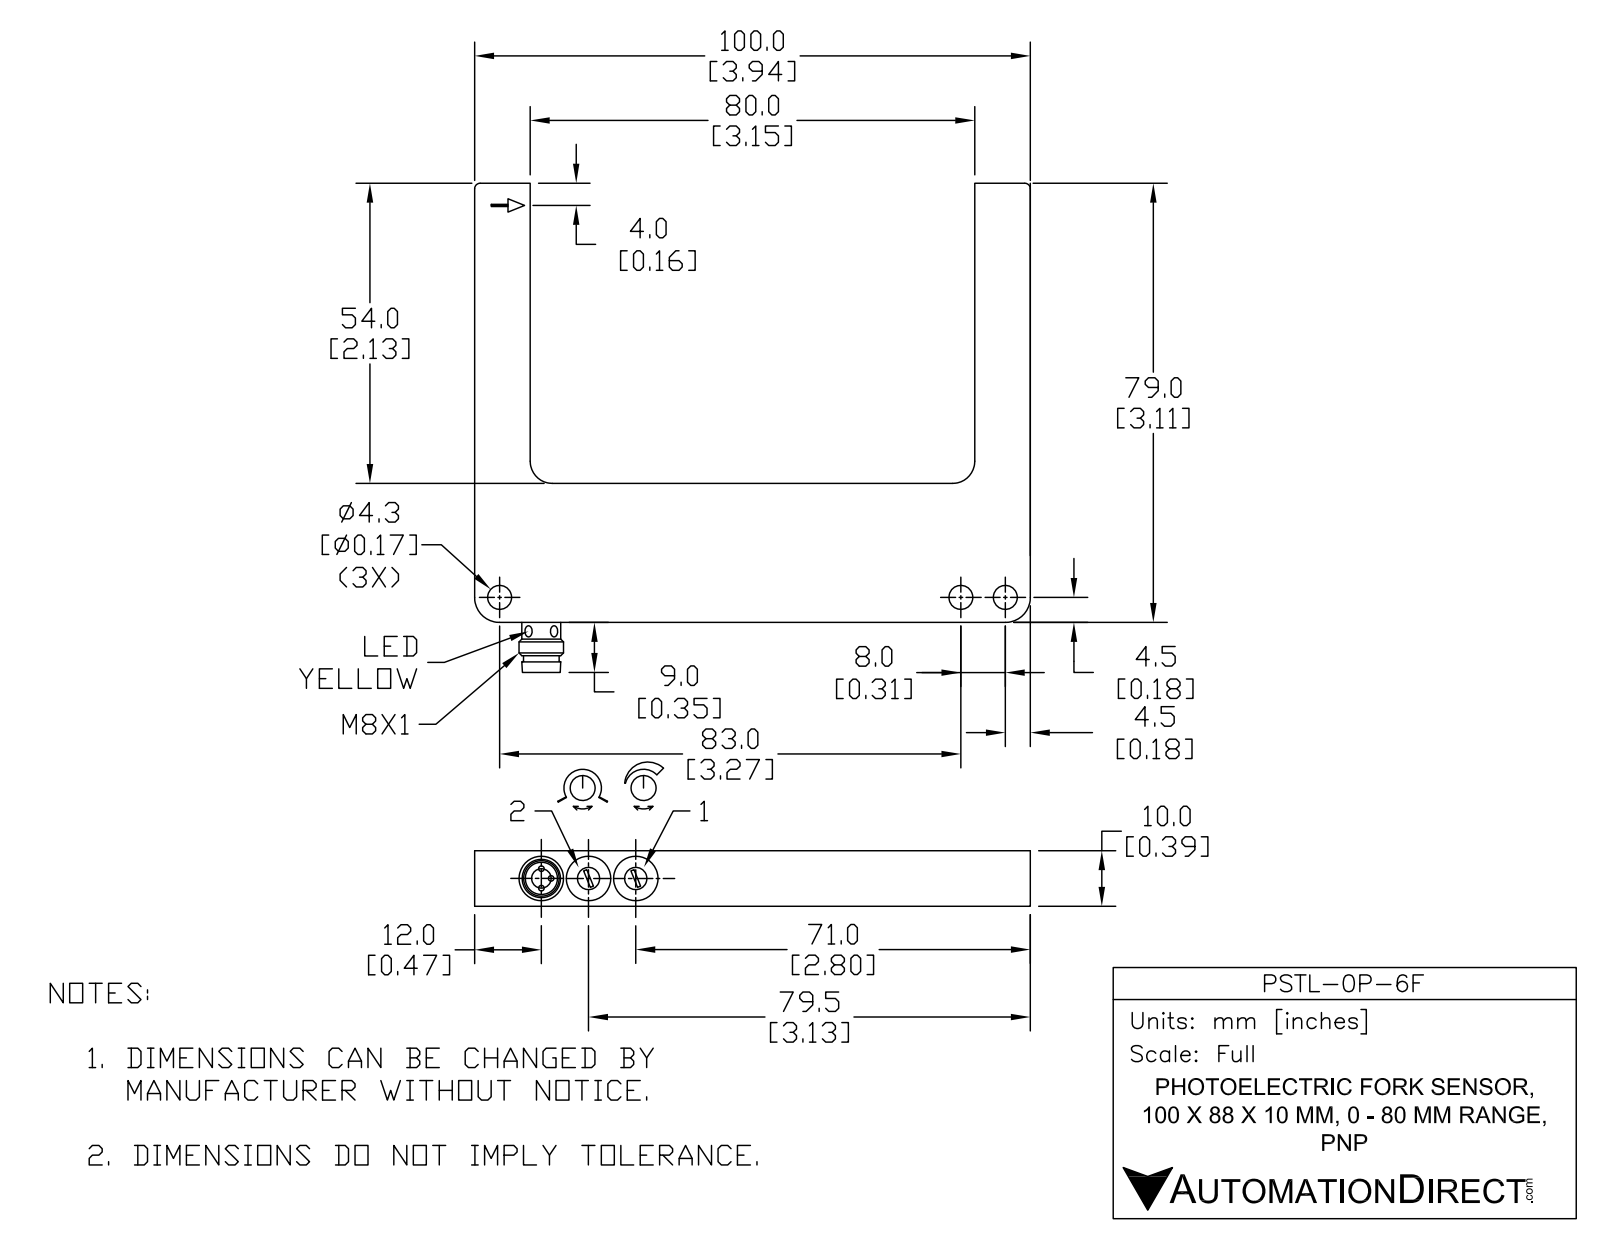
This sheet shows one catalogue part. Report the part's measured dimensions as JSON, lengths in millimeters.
{"part_name": "PSTL-0P-6F", "step_written_by": "SolidWorks 2019 (AUTOMOTIVE_DESIGN)", "units": "millimeters", "bodies": {"solids": 1, "faces": 95, "planar": 35, "cylindrical": 48, "other": 12}, "overall_size": [100, 88, 10], "volume_mm3": 35560, "surface_area_mm2": 12420, "round_holes": [[4.3, 3], [2, 2], [4, 2], [8, 2], [5.8, 1]], "round_bosses_or_shafts": [[1, 3], [8, 1], [6.8, 1]], "partial_cylinders_radius": [[0.5, 2], [1, 2], [1.6, 2], [4, 2], [4.5, 2]], "face_to_face_distances": [10, 90, 100, 25, 80, 54, 79, 78.9, 24.9, 4], "hole_center_spacings": [8.5, 8, 17, 83, 91]}
